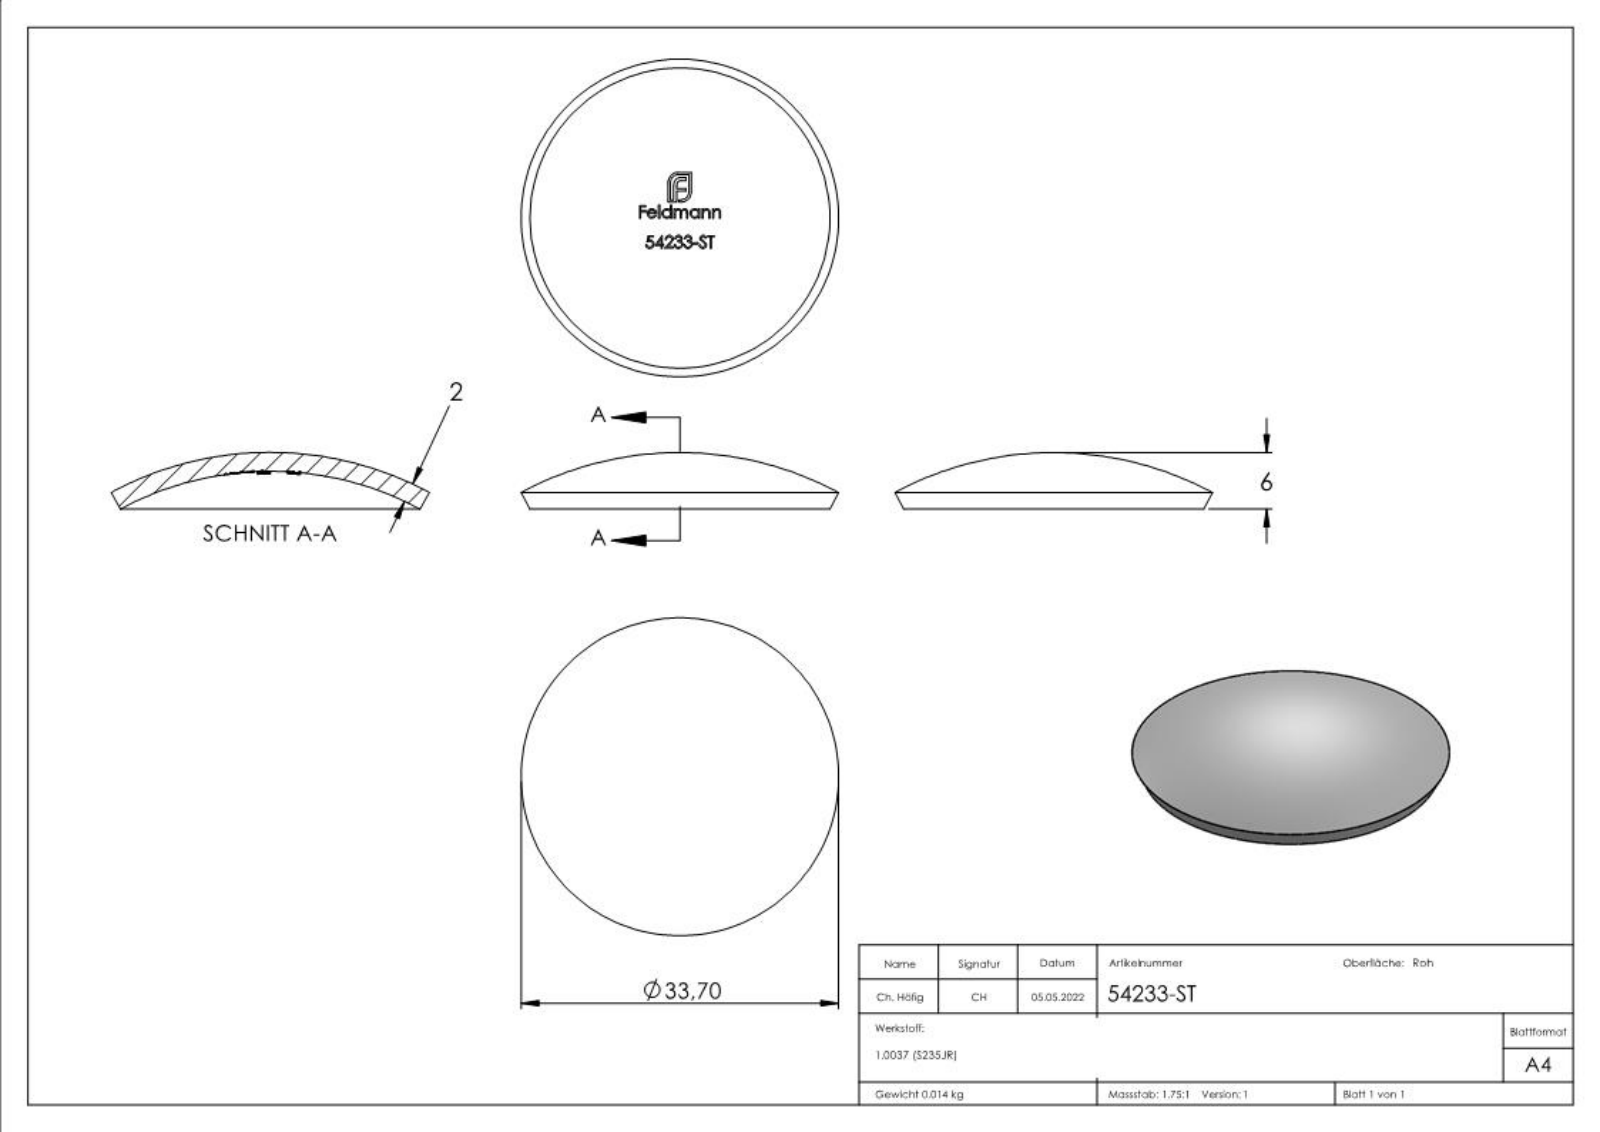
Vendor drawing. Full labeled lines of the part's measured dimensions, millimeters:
Part name (STEP PRODUCT): 54233-ST
STEP written by: SolidWorks 2018 (CONFIG_CONTROL_DESIGN)
Units: millimetres
Bodies: 1 solid, 270 faces (121 planar, 0 cylindrical, 149 other)
Overall size (bounding box): 33.7 × 33.7 × 6
Volume: 1 791 mm³ · Surface area: 2 011 mm²
Main face-to-face distances: 4.23, 1.26, 1.14, 0.99, 0.63, 0.58, 0.34, 2.02, 5.48, 3.96
